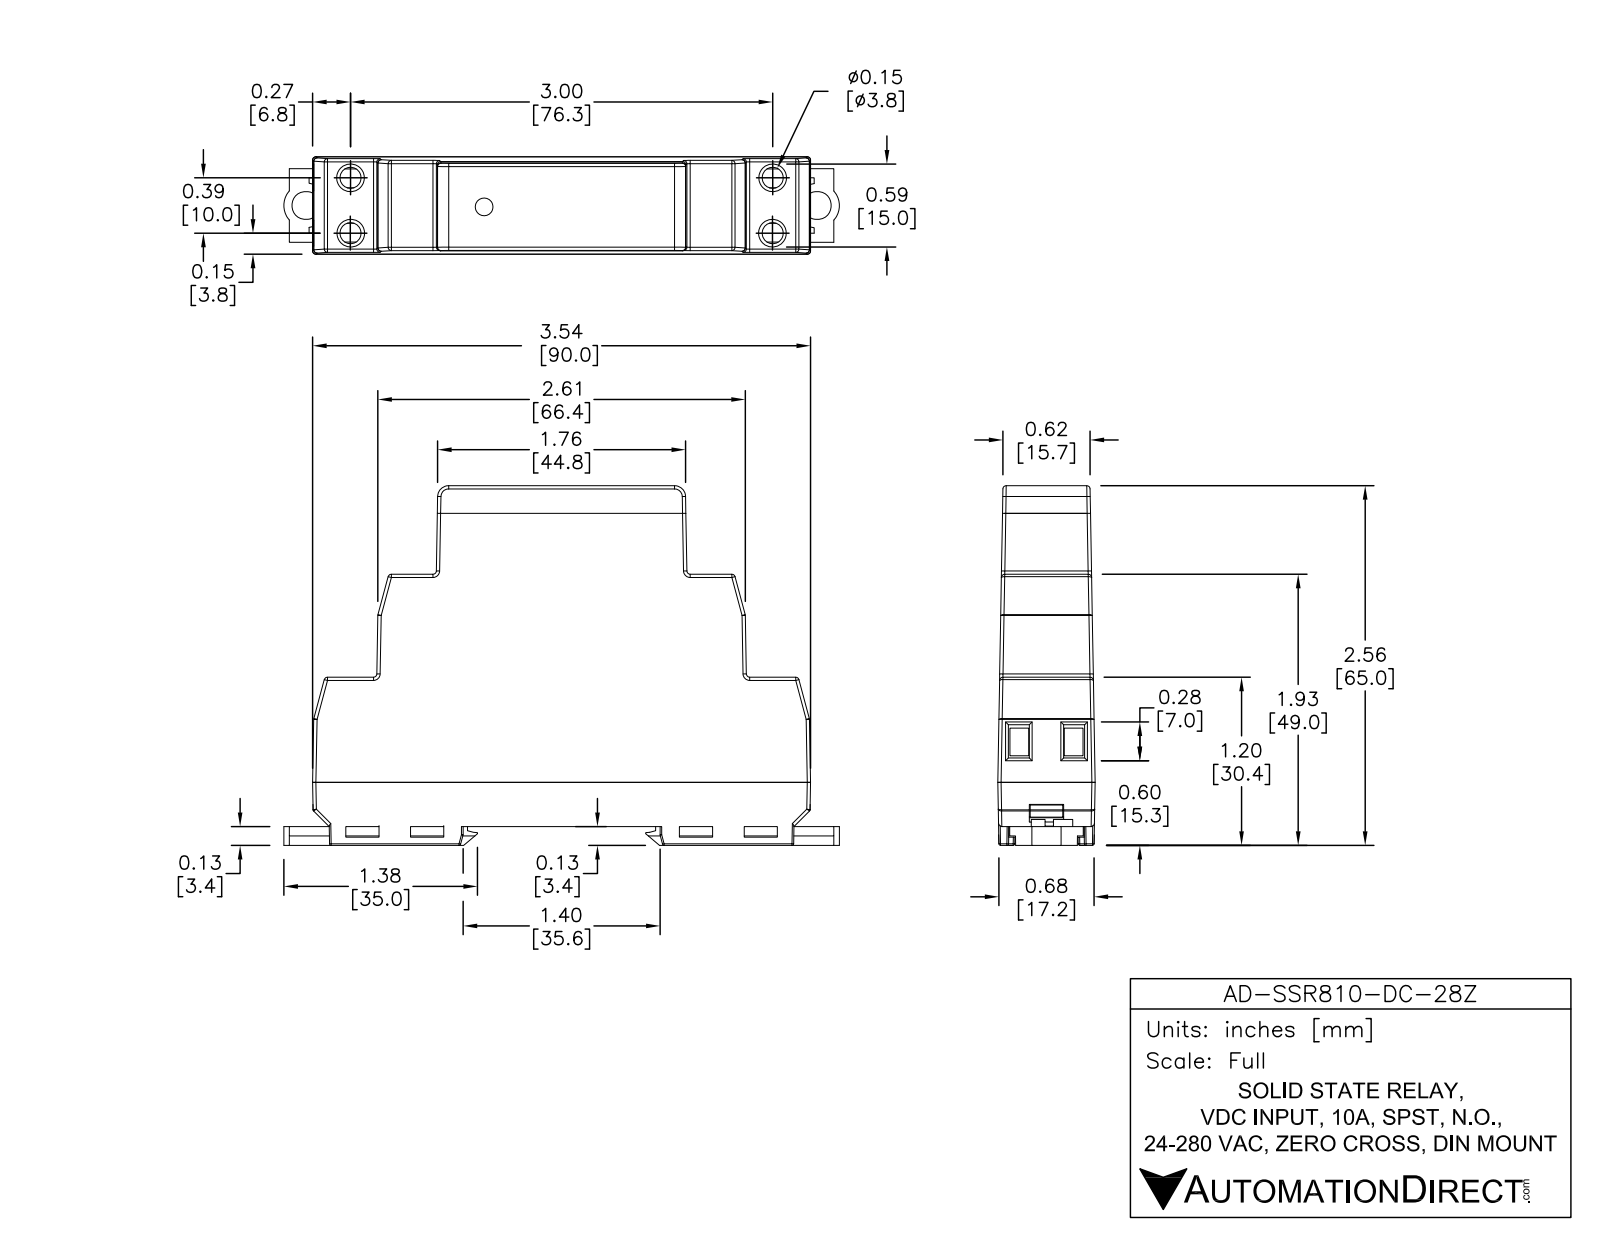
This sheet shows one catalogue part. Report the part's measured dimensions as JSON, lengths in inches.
{"part_name": "AD-SSR810-DC-28Z", "step_written_by": "SolidWorks 2013 (AUTOMOTIVE_DESIGN)", "units": "inches", "bodies": {"solids": 1, "faces": 836, "planar": 489, "cylindrical": 78, "other": 269}, "overall_size": [3.924, 2.616, 0.685], "volume_in3": 4.605, "surface_area_in2": 24.23, "round_holes": [[0.19, 4], [0.2, 2]], "round_bosses_or_shafts": [[0.105, 1]], "partial_cylinders_radius": [[0.015, 41], [0.06, 2], [0.172, 2]], "face_to_face_distances": [2.525, 0.049, 2.574, 0.425, 2.215, 0.025, 0.05, 1.934, 1.885, 0.64], "hole_center_spacings": [0.338, 3.3, 0.364, 3.01, 3.032, 3.58]}
